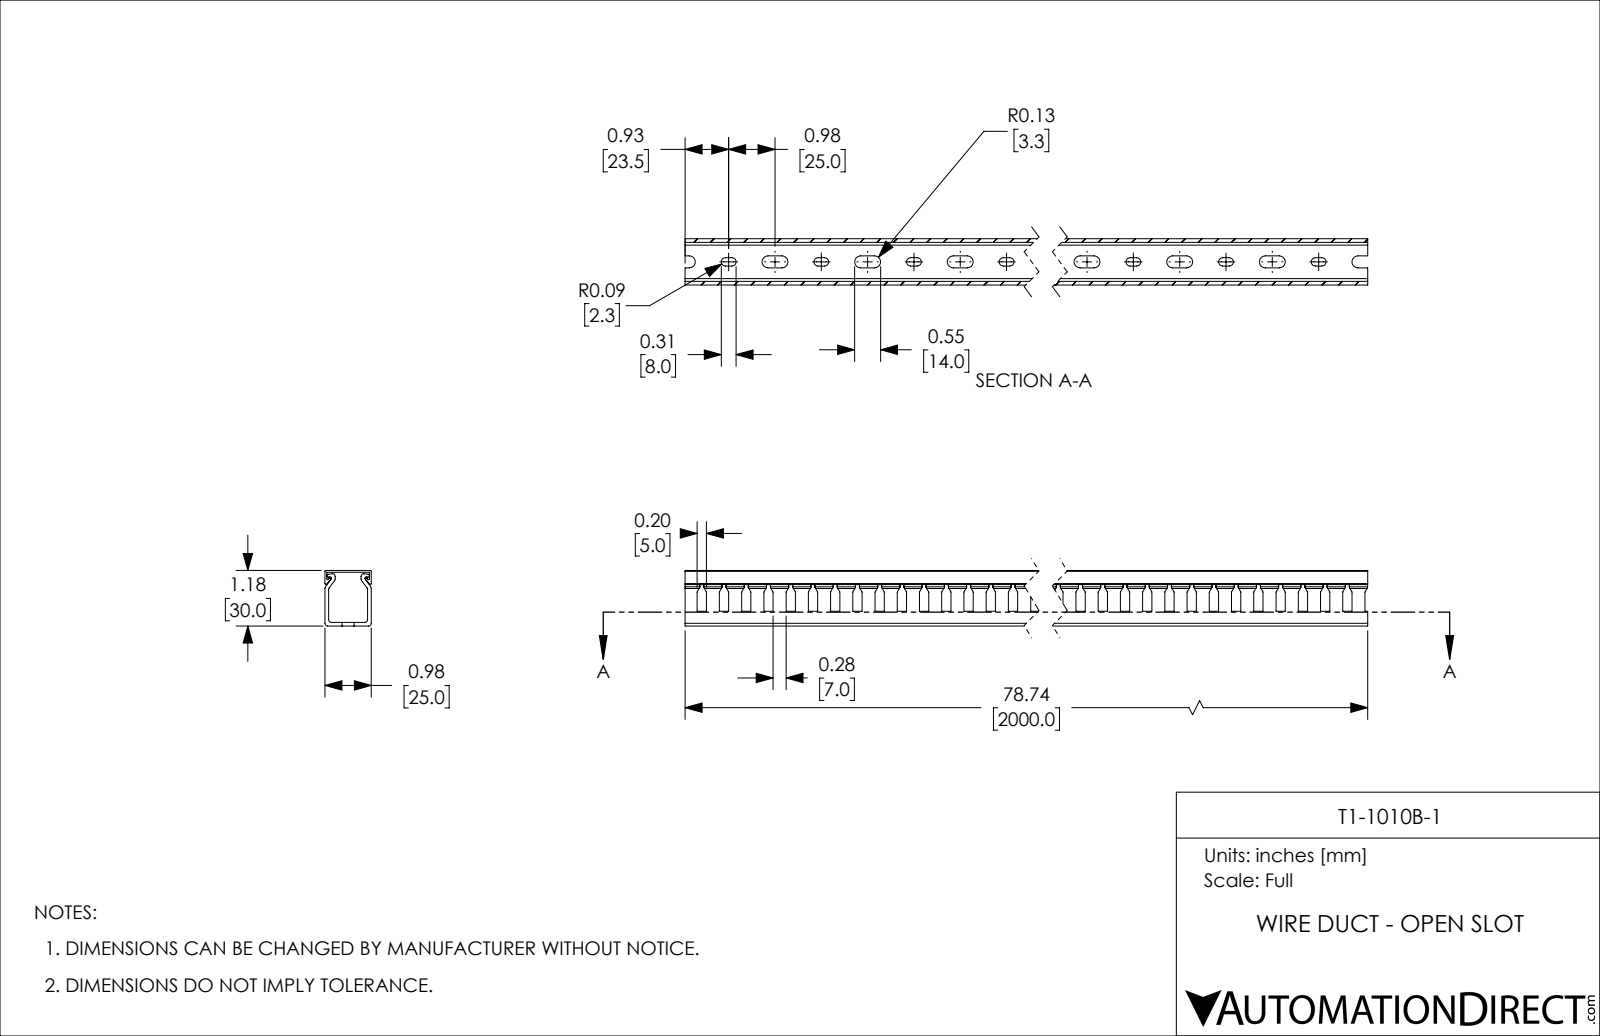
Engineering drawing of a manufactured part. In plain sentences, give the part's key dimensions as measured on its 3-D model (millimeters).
The part is named "T1-1010B-1". Its 3-D file was written by "SolidWorks 2021 (CONFIG_CONTROL_DESIGN)". It is 2 solids with 945 faces: 514 planar, 431 cylindrical and 0 other. Overall it measures 2000 by 30 by 25 millimeters. Its volume is 407 568 cubic millimeters and its surface area 496 758 square millimeters. Partial cylindrical surfaces (rounded edges, fillets, slot ends): 80 of radius 2.25, 80 of radius 3.25, 12 of radius 1.5, 8 of radius 0.5, 6 of radius 0.75. The main face-to-face distances are 2, 1, 23, 25, 29, 30, 21, 27, 28, 24.
